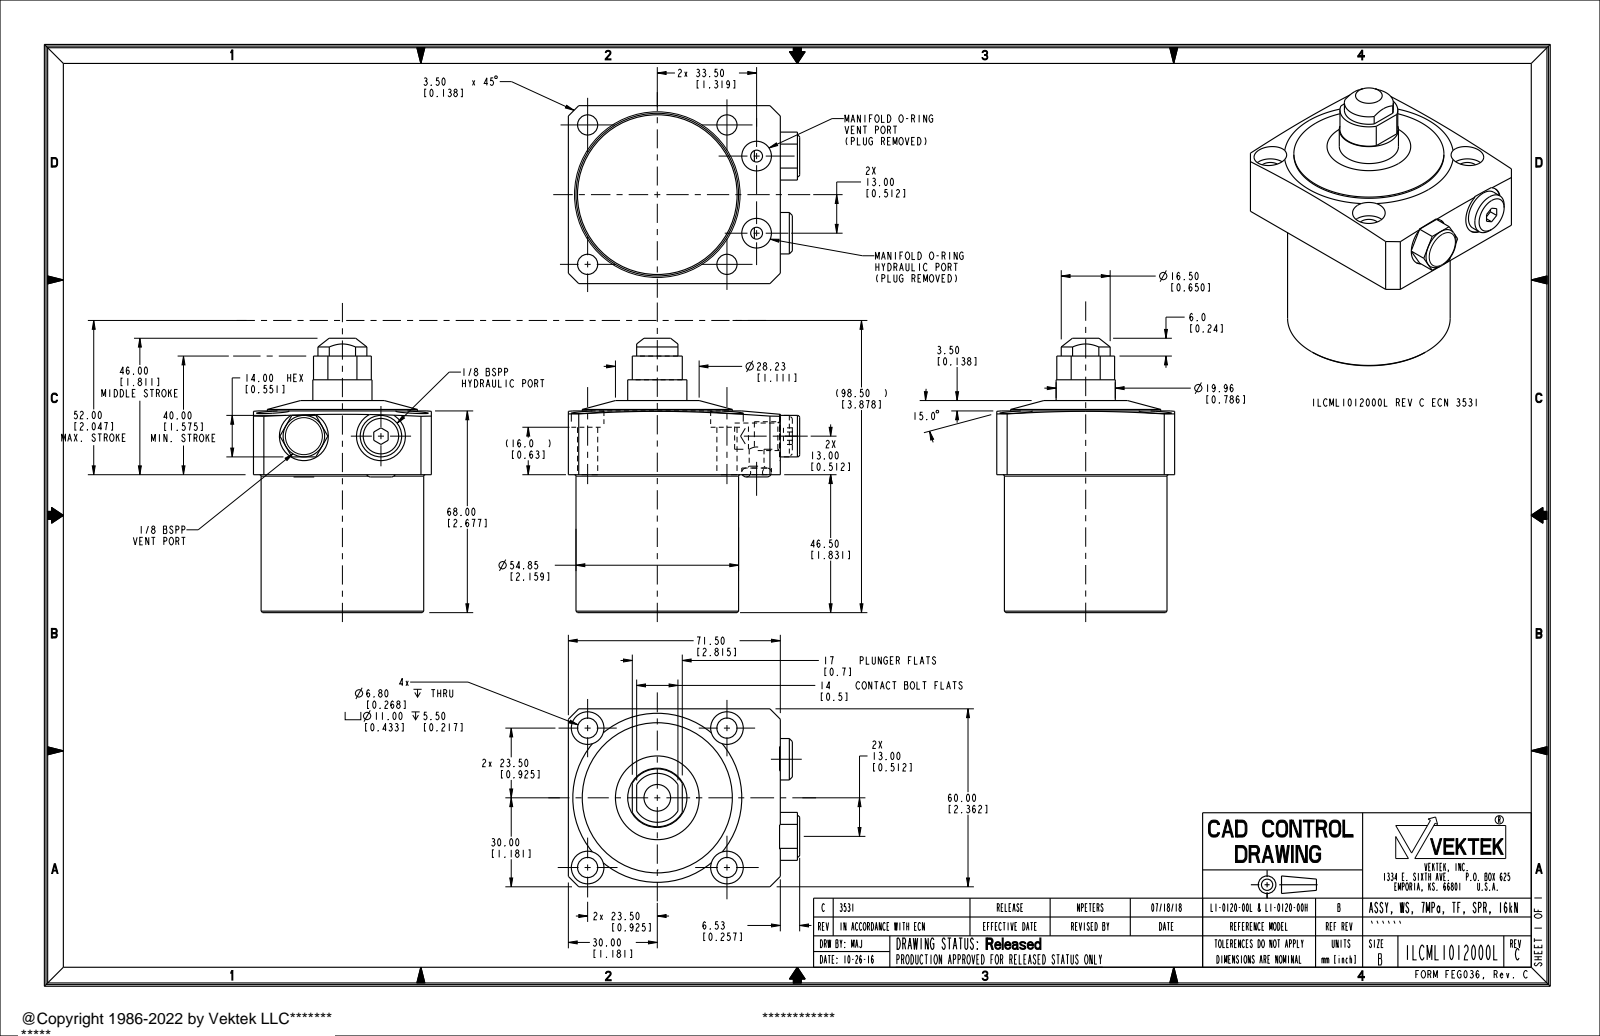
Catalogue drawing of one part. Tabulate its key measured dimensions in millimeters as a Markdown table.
| quantity | value |
| --- | --- |
| part name | ILCML1012000L |
| STEP written by | PRO/ENGINEER BY PARAMETRIC TECHNOLOGY CORPORATION, 2013320 (AUTOMOTIVE_DESIGN) |
| units | millimeters |
| bodies | 4 solids, 137 faces (55 planar, 50 cylindrical, 32 other) |
| overall size | 92.5 × 78.03 × 60 |
| volume | 205 838 mm³ |
| surface area | 27 930 mm² |
| round holes (diameter × count) | 6.8 × 4, 11 × 4, 5 × 2, 6 × 2, 8.84 × 2, 10 × 2, 16.5 × 2 |
| round bosses / shafts (diameter × count) | 54.85 × 1, 50.62 × 1, 19.96 × 1, 13.97 × 1, 9.73 × 1, 9.72 × 1 |
| partial cylindrical surfaces (radius × count) | 8.25 × 1, 9.75 × 1 |
| main face-to-face distances | 46.5, 60, 71.5, 68, 21.5, 25, 3.5, 71.25, 16, 62.5 |
| hole center spacings | 47, 14.5, 26, 37.85, 57.96, 66.47, 67.68 |
